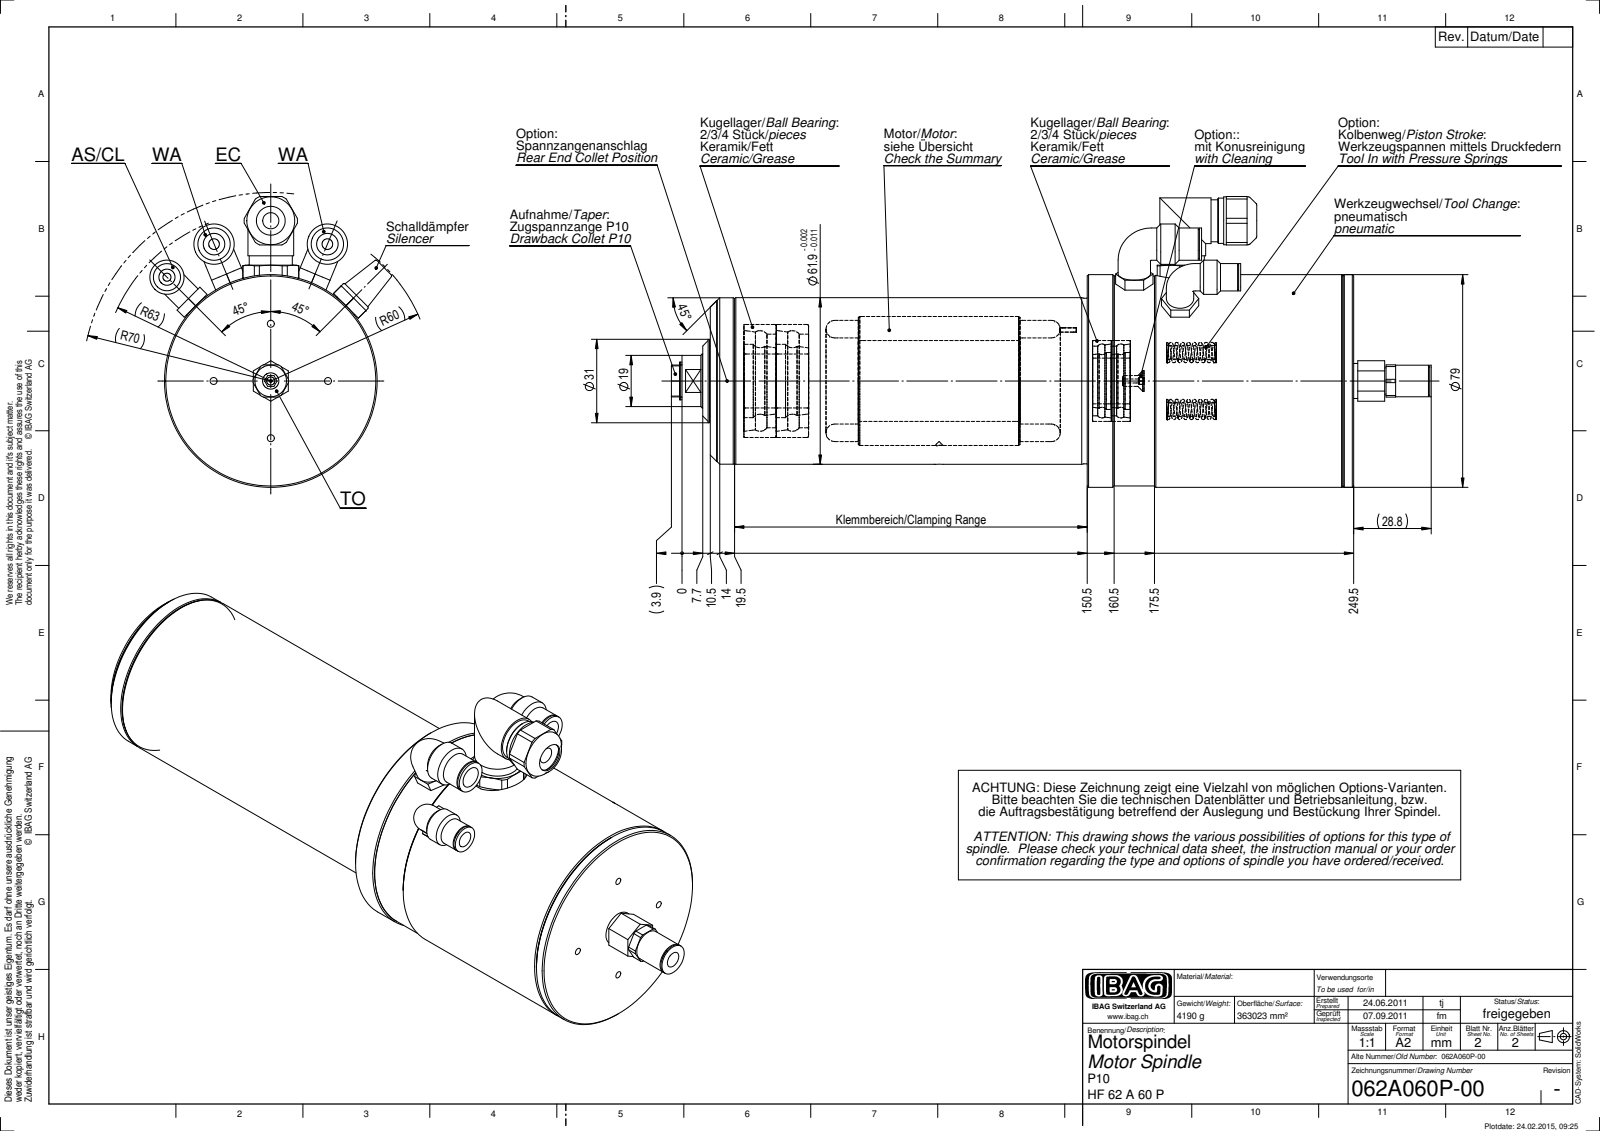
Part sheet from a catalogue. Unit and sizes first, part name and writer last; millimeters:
Units: millimetres
Overall size (bounding box): 282.25 × 109.5 × 89.8
Round holes (diameter × count): ⌀2.1 ×4, ⌀2.6 ×4, ⌀4 ×4, ⌀6 ×3, ⌀8 ×3, ⌀2 ×1, ⌀3.3 ×1, ⌀10.7 ×1
Round bosses / shafts (diameter × count): ⌀12 ×4, ⌀5.7 ×4, ⌀17 ×2, ⌀15 ×2, ⌀13 ×2, ⌀10.16 ×2, ⌀79 ×1, ⌀78 ×1
Partial cylindrical surfaces — rounded edges, fillets, slot ends (radius × count): R6.6 ×1, R9.9 ×1, R10.4 ×1
Main face-to-face distances: 74, 15, 89, 147.5, 162.5, 236.5, 6.5, 141, 156, 230
Hole centre spacings: 24.16, 34.5, 9.75, 11.5, 16.26, 19.29, 21.25, 25.21
Bodies: 0 solids, 411 faces (161 planar, 151 cylindrical, 99 other)
Part name (STEP PRODUCT): 062A060P-00
STEP written by: SolidWorks 2010 (CONFIG_CONTROL_DESIGN)
